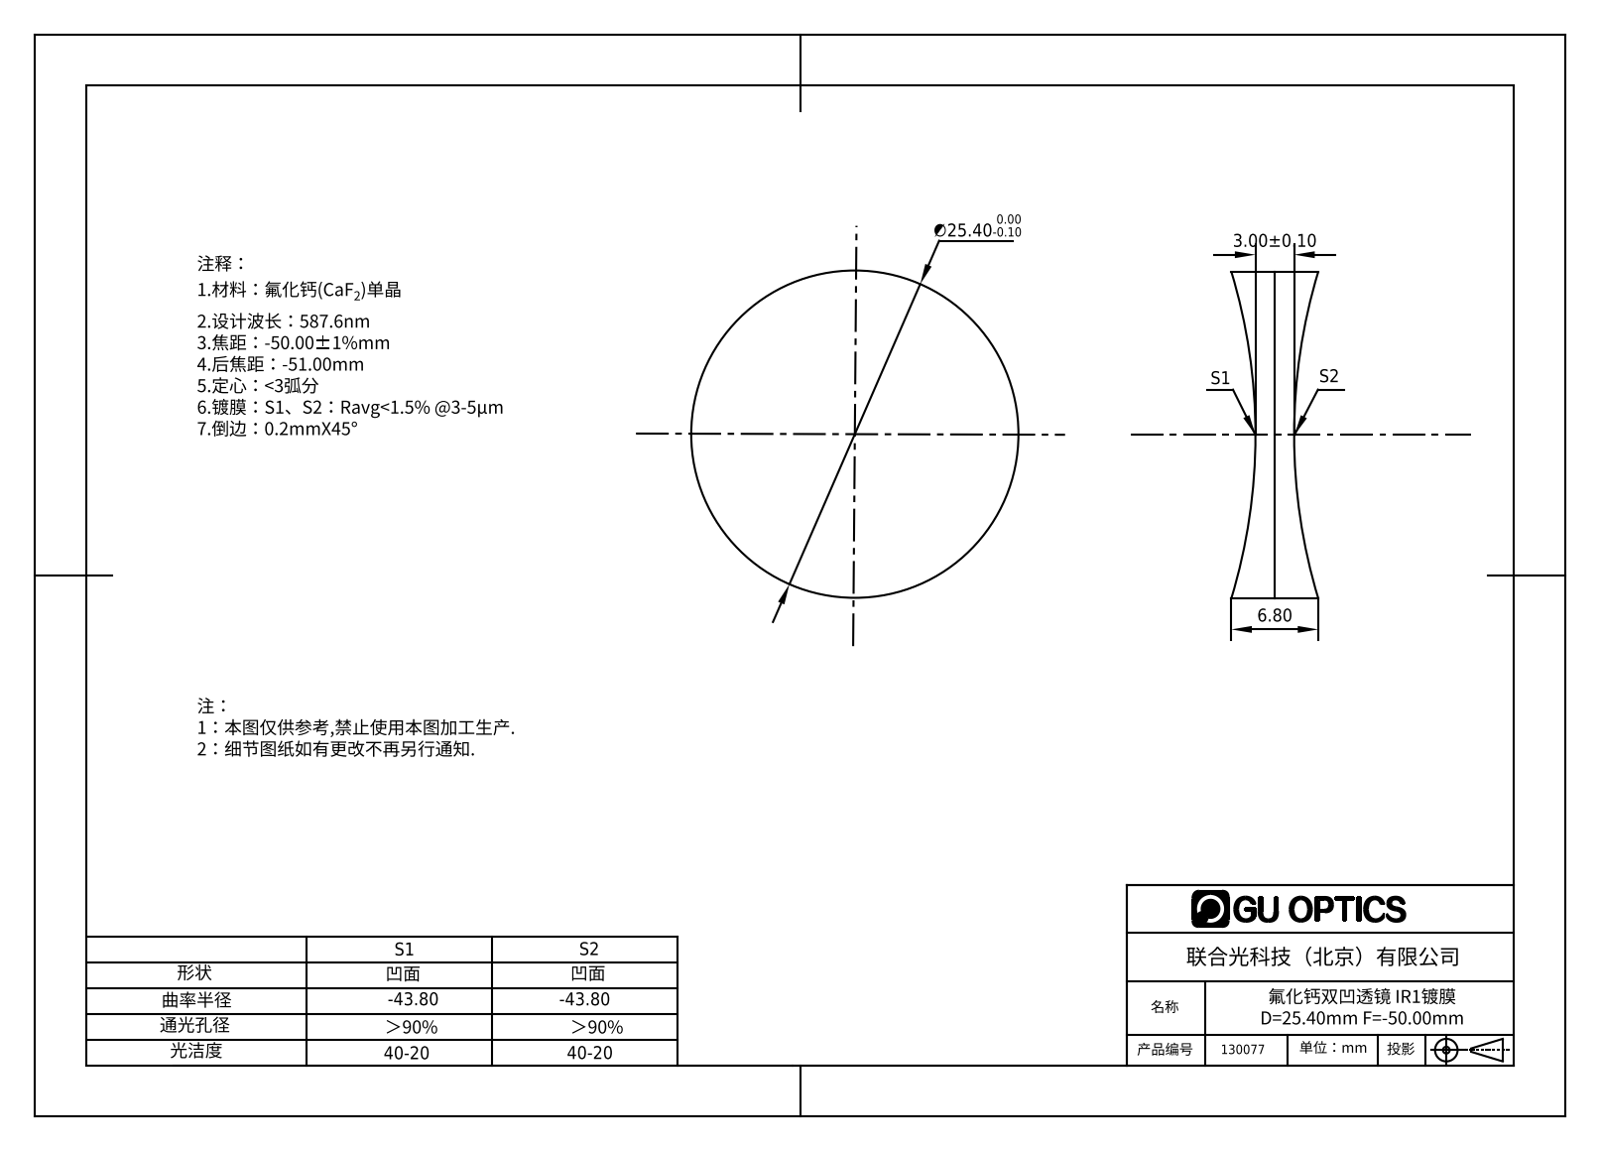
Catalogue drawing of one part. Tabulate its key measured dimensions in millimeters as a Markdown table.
| quantity | value |
| --- | --- |
| part name | 130073 |
| STEP written by | SolidWorks 2016 (AUTOMOTIVE_DESIGN) |
| units | millimeters |
| bodies | 1 solid, 6 faces (0 planar, 2 cylindrical, 4 other) |
| overall size | 25.4 × 25.4 × 6.76 |
| volume | 2 467 mm³ |
| surface area | 1 575 mm² |
| round bosses / shafts (diameter × count) | 25.4 × 1 |
